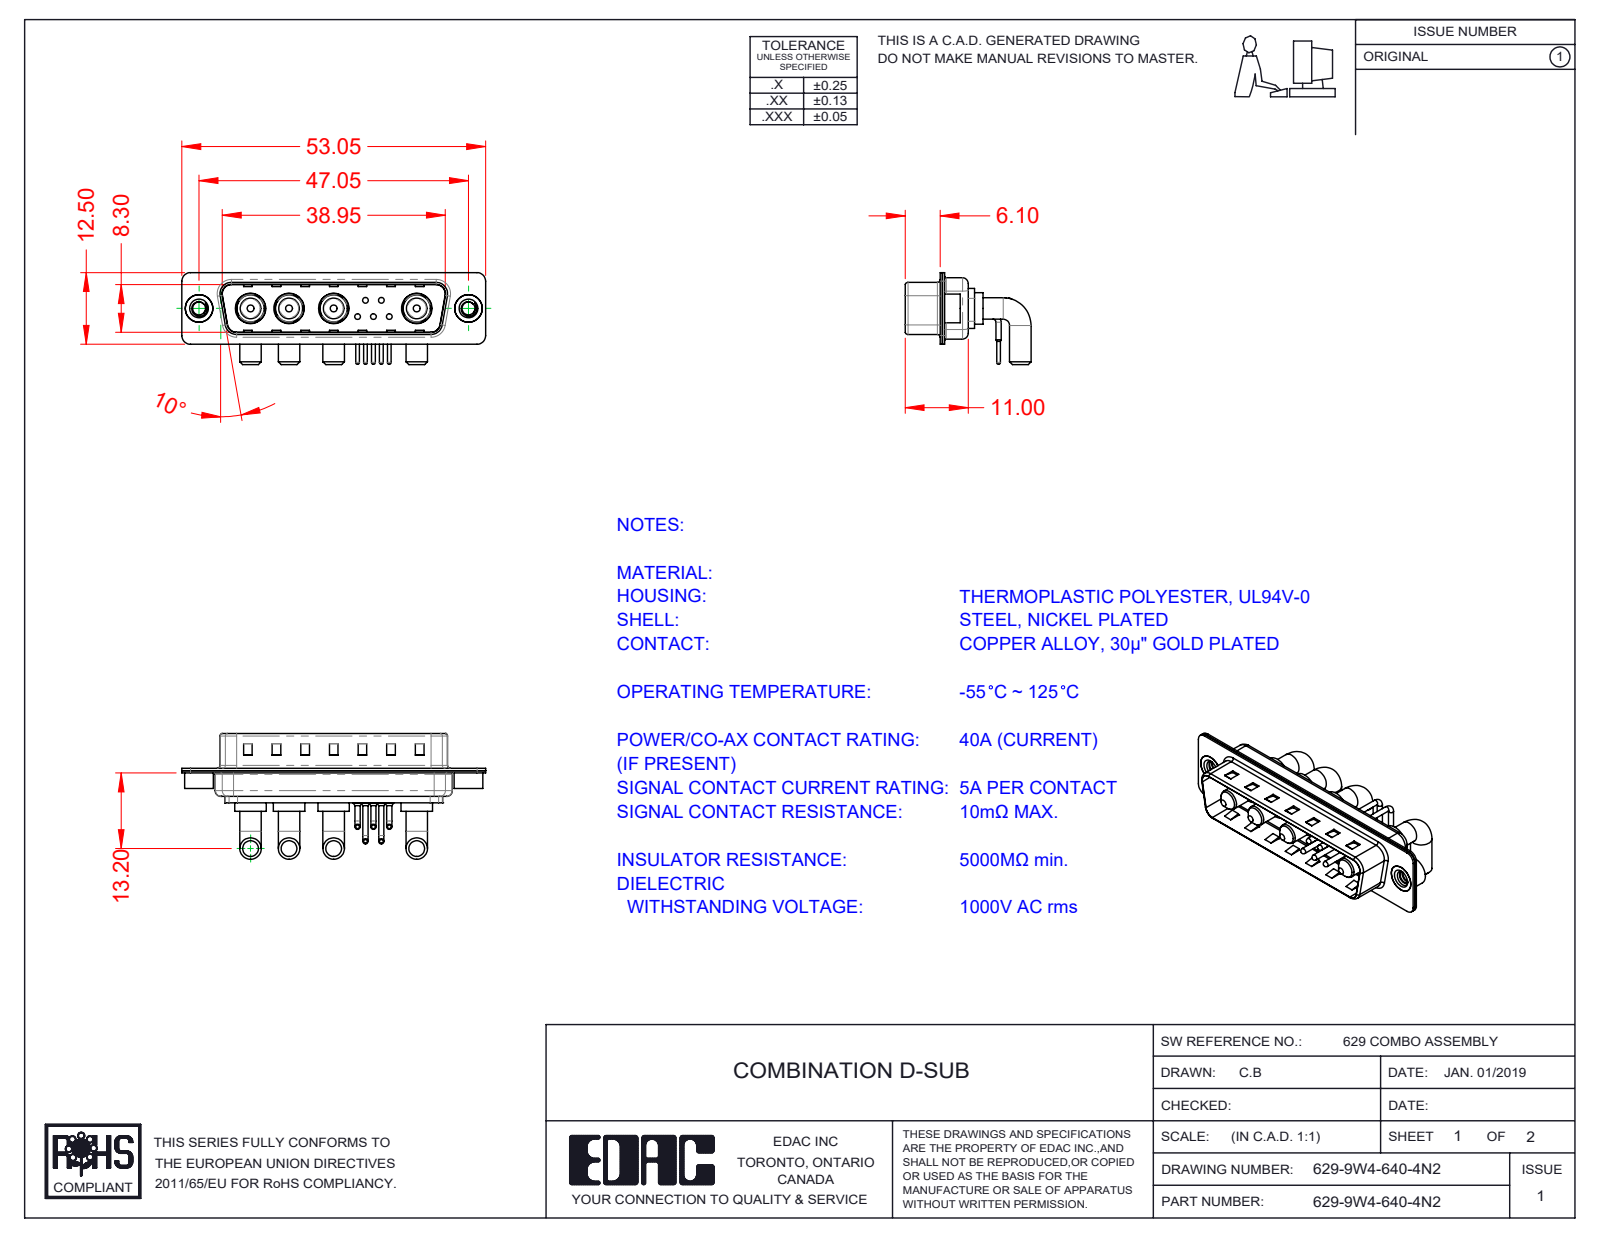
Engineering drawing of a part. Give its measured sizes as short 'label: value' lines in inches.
name: 629Combo Shell Rear_25 Contacts; 629-9W4-640-4N2; 629Combo Housing_9W4; 629Combo Shell Front_25 Contacts (+4 more)
written by: SolidWorks 2020 (CONFIG_CONTROL_DESIGN)
unit: in
bodies: 18 solids, 1098 faces (531 planar, 401 cylindrical, 166 other)
size: 2.089 × 0.865 × 0.632
volume: 0.22 in³; area: 11.51 in²
holes: 5× ⌀0.03, 5× ⌀0.063, 5× ⌀0.079, 4× ⌀0.191, 4× ⌀0.209, 2× ⌀0.089, 2× ⌀0.157, 2× ⌀0.189
bosses: 10× ⌀0.035, 8× ⌀0.148, 5× ⌀0.059, 5× ⌀0.039, 5× ⌀0.026, 4× ⌀0.217, 4× ⌀0.205, 4× ⌀0.187
rounds: 16× R0.059, 12× R0.079, 8× R0.02, 8× R0.063, 5× R0.04, 4× R0.01, 4× R0.024, 4× R0.026
face distances: 0.016, 0.031, 0.374, 0.358, 0.343, 0.39, 0.03, 0.047, 0.22, 0.014
hole spacings: 0.124, 0.109, 0.198, 0.571, 0.109, 0.173, 0.174, 0.197
